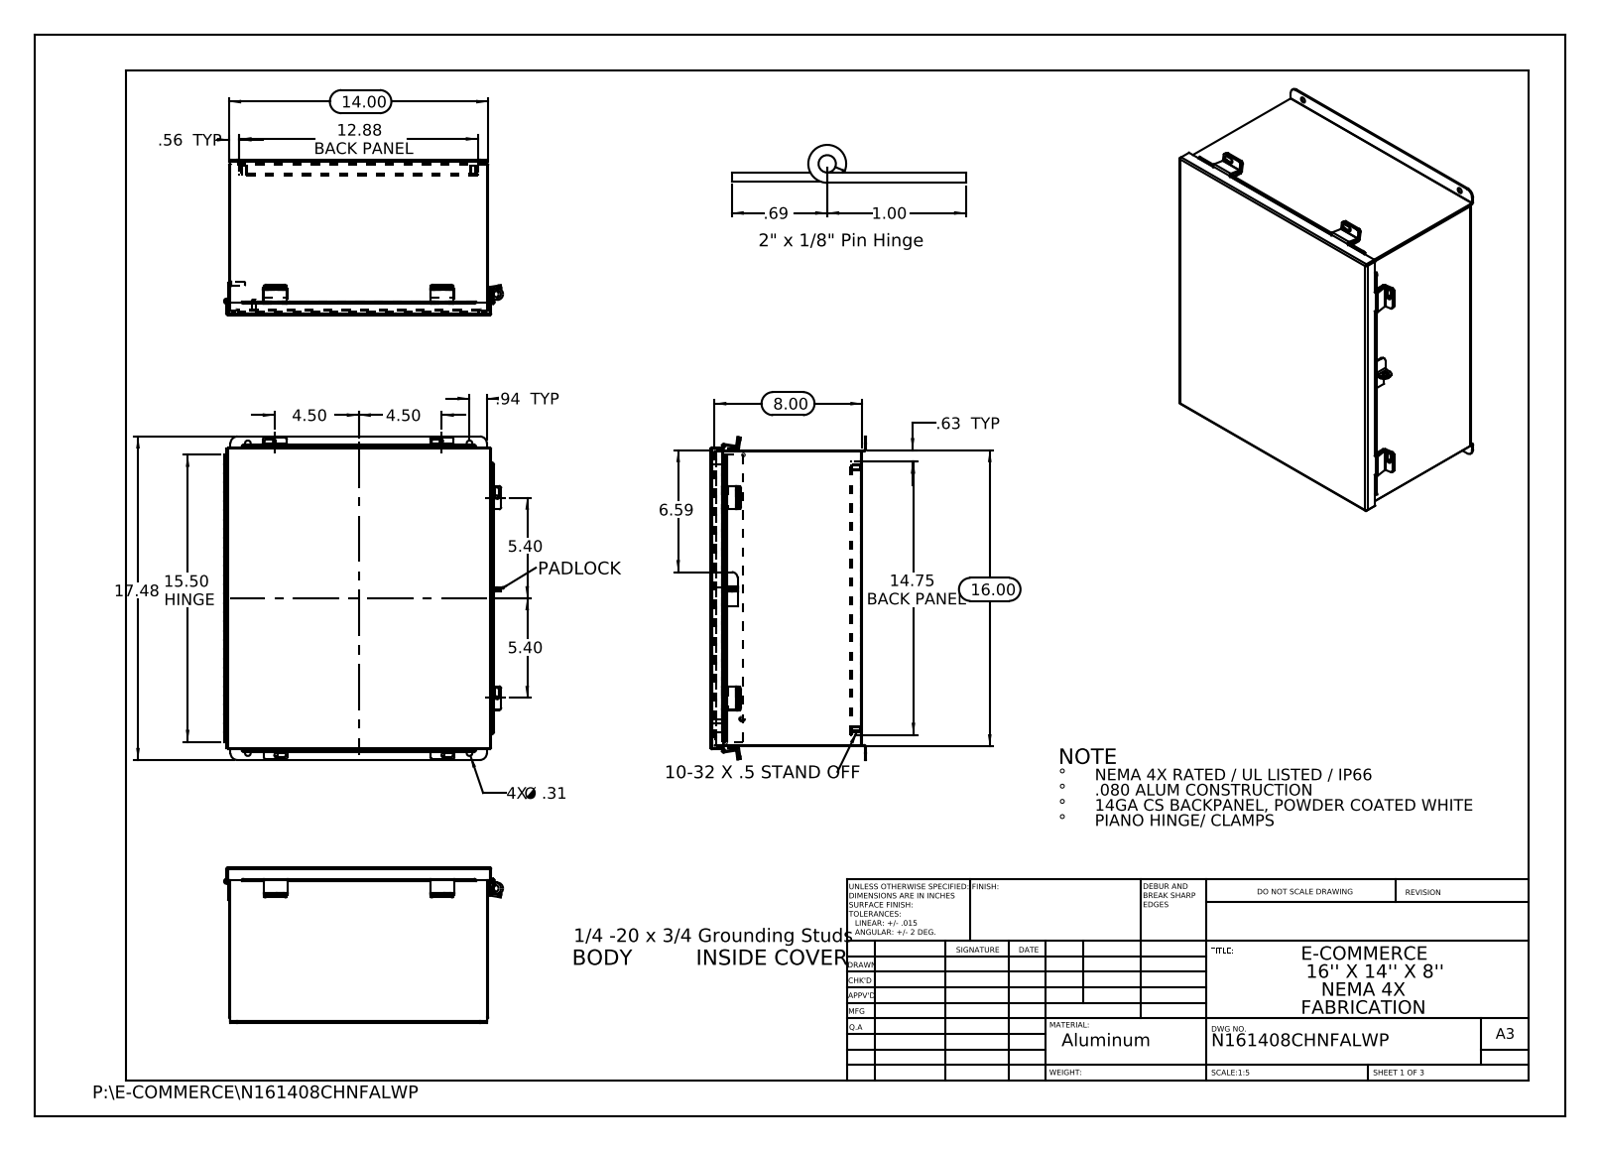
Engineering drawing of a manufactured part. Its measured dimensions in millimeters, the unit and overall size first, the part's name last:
Units: millimetres
Overall size (bounding box): 443.9 × 382.8 × 213.1
Round holes (diameter × count): ⌀6.4 ×10, ⌀4.7 ×4, ⌀7.9 ×4, ⌀3.2 ×1, ⌀3.2 ×1, ⌀9.5 ×1, ⌀9.5 ×1
Round bosses / shafts (diameter × count): ⌀8 ×4, ⌀8 ×2, ⌀6 ×2, ⌀6.9 ×1, ⌀6.4 ×1
Partial cylindrical surfaces — rounded edges, fillets, slot ends (radius × count): R3.2 ×23, R0.3 ×13, R0.2 ×12, R2.2 ×12, R3.4 ×12, R2.1 ×6, R2.5 ×6, R9.5 ×4
Main face-to-face distances: 1.9, 206.5, 353.7, 404.5, 204.5, 208.4, 193.8, 14.6, 12.7, 191.8
Hole centre spacings: 33.4, 311, 391.8, 499.2, 228.6, 304.2, 314.3, 358.8
Volume: 1 536 000 mm³ · Surface area: 1 643 000 mm²
Bodies: 27 solids, 866 faces (539 planar, 307 cylindrical, 20 other)
Part name (STEP PRODUCT): N161408CHNFALWP Hinge Cover Side JIC; N161408CHNFALWP _JIC Hinge; HW-CLH-JH-20154; N161408CHNFALWP JIC Backpanel (+8 more)
STEP written by: SolidWorks 2013 (CONFIG_CONTROL_DESIGN)
